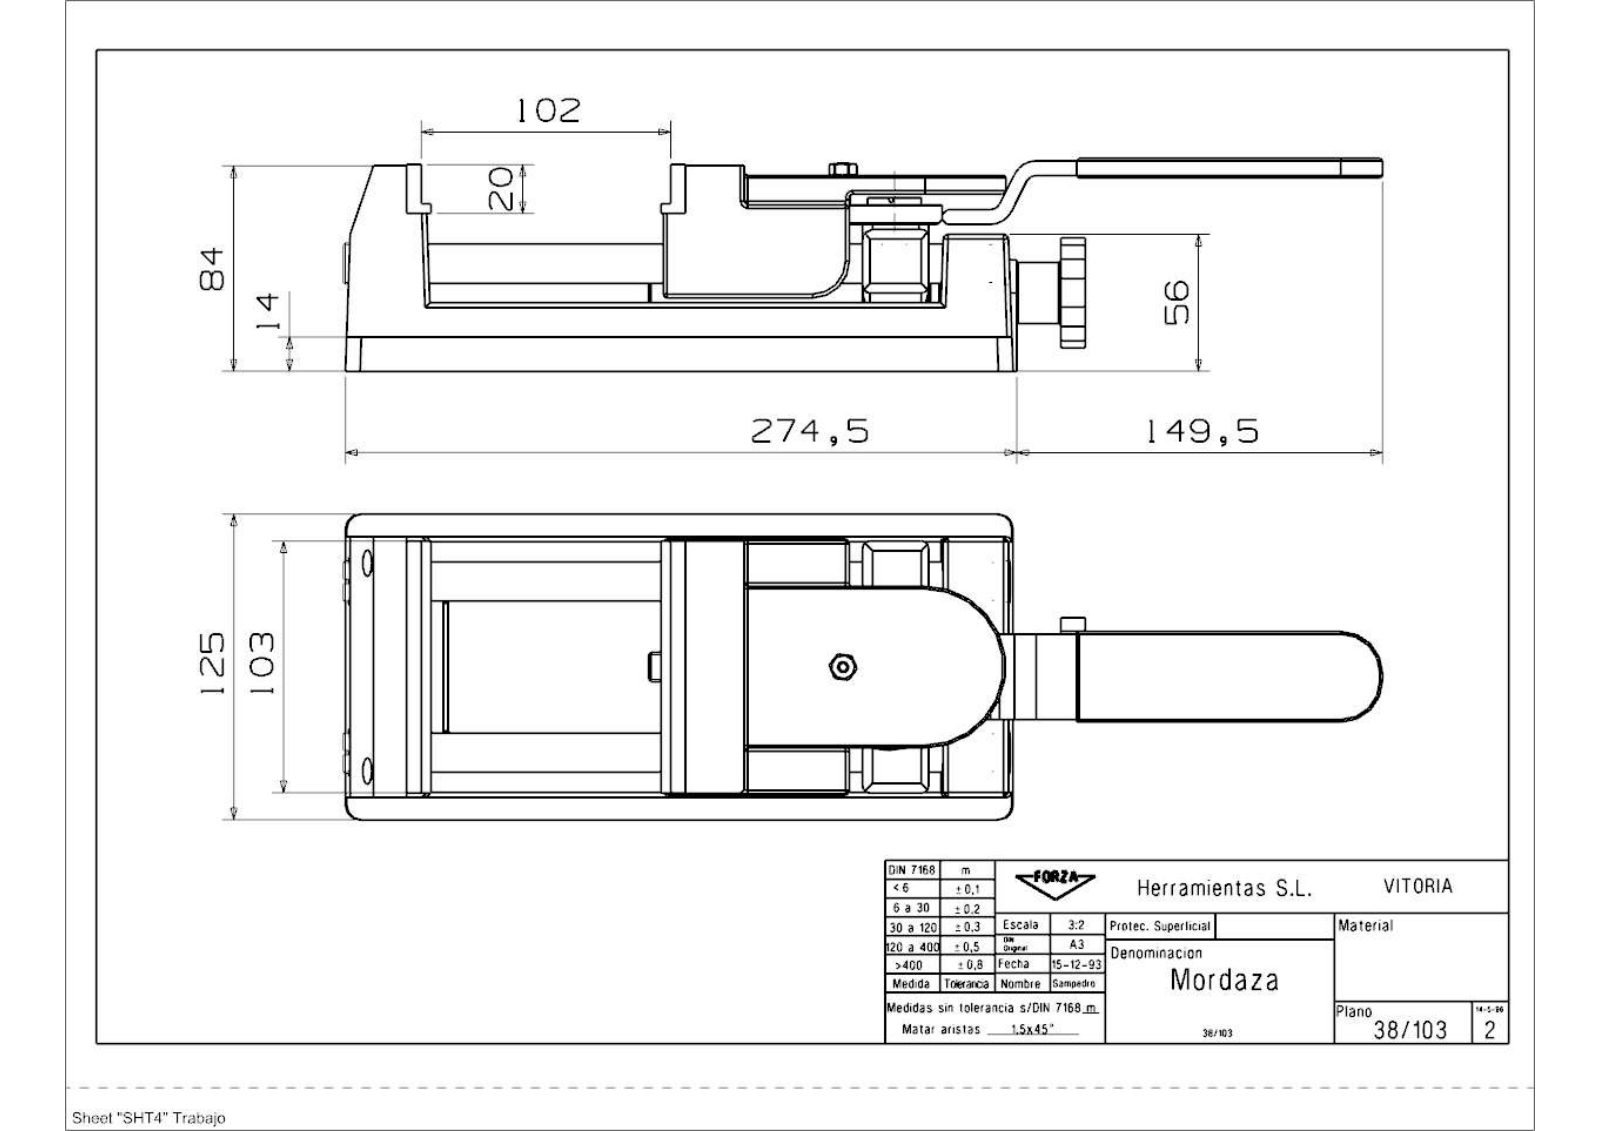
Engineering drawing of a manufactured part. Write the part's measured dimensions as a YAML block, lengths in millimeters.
part_name: "38_103_Mordaza"
step_written_by: "SIEMENS PLM Software NX 7.5 (AUTOMOTIVE_DESIGN)"
units: millimeters
bodies: {solids: 16, faces: 497, planar: 176, cylindrical: 204, other: 117}
overall_size: [412.49, 125, 88]
volume: 1335000
surface_area: 266972
round_holes:
  - {diameter: 5.19, count: 3}
  - {diameter: 16, count: 3}
  - {diameter: 3, count: 2}
  - {diameter: 6.5, count: 2}
  - {diameter: 11, count: 2}
  - {diameter: 16.1, count: 2}
  - {diameter: 16.19, count: 2}
  - {diameter: 5, count: 1}
  - {diameter: 5.9, count: 1}
  - {diameter: 8, count: 1}
  - {diameter: 8.78, count: 1}
  - {diameter: 10.2, count: 1}
round_bosses_or_shafts:
  - {diameter: 35, count: 1}
  - {diameter: 25, count: 1}
  - {diameter: 22, count: 1}
  - {diameter: 19, count: 1}
  - {diameter: 15.9, count: 1}
  - {diameter: 12, count: 1}
  - {diameter: 9.73, count: 1}
  - {diameter: 9, count: 1}
partial_cylinders:
  - {radius: 1.5, count: 35}
  - {radius: 2, count: 28}
  - {radius: 4, count: 14}
  - {radius: 1, count: 10}
  - {radius: 3, count: 8}
  - {radius: 10, count: 8}
  - {radius: 5, count: 6}
  - {radius: 5.5, count: 6}
face_to_face_distances: [28, 1, 14, 56, 26, 3, 25.25, 81.25, 80, 52]
hole_center_spacings: [33.35, 37, 40.31, 44.3, 61.53, 84.04, 19.5, 21.5]
